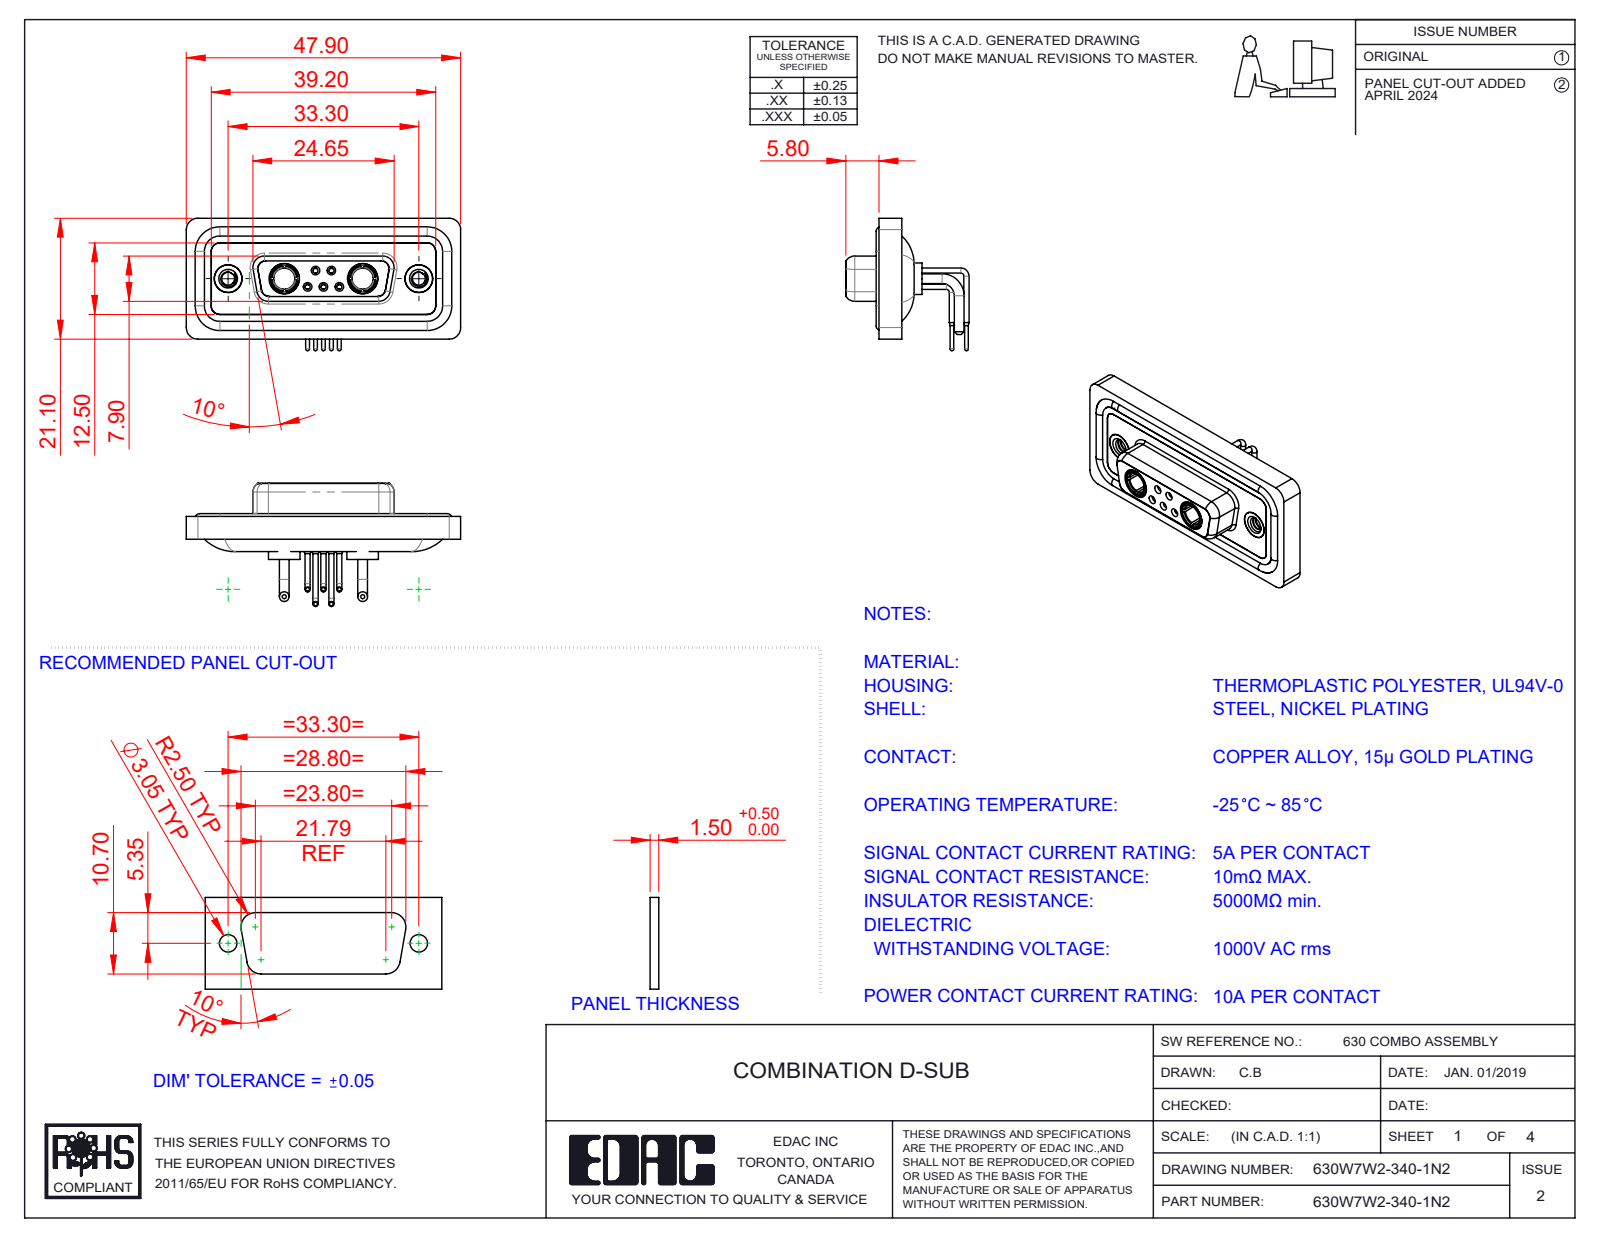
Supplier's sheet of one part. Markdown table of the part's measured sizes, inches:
| quantity | value |
| --- | --- |
| part name | 630Combo Shell Front_15 Contacts; 630Combo Threaded Rivet_2; Power Socket_10A RA; 630Combo Waterproof Housing_15 Contacts (+5 more) |
| STEP written by | SolidWorks 2023 (CONFIG_CONTROL_DESIGN) |
| units | inches |
| bodies | 16 solids, 807 faces (238 planar, 353 cylindrical, 216 other) |
| overall size | 1.886 × 0.91 × 0.848 |
| volume | 0.371 in³ |
| surface area | 15.66 in² |
| round holes (diameter × count) | 0.035 × 5, 0.043 × 5, 0.059 × 5, 0.079 × 5, 0.191 × 4, 0.063 × 3, 0.067 × 2, 0.089 × 2, 0.146 × 2, 0.157 × 2, 0.159 × 2, 0.197 × 2 |
| round bosses / shafts (diameter × count) | 0.063 × 6, 0.035 × 5, 0.026 × 5, 0.067 × 4, 0.217 × 2, 0.205 × 2, 0.195 × 2, 0.195 × 2 |
| partial cylindrical surfaces (radius × count) | 0.079 × 20, 0.059 × 18, 0.053 × 12, 0.063 × 8, 0.01 × 4, 0.02 × 4, 0.024 × 4, 0.026 × 4 |
| main face-to-face distances | 0.016, 0.071, 0.043, 0.063, 0.098, 0.114, 0.122, 0.146, 0.161, 0.059 |
| hole center spacings | 0.124, 0.109, 0.386, 0.925, 0.17, 0.17, 0.198, 0.198 |
